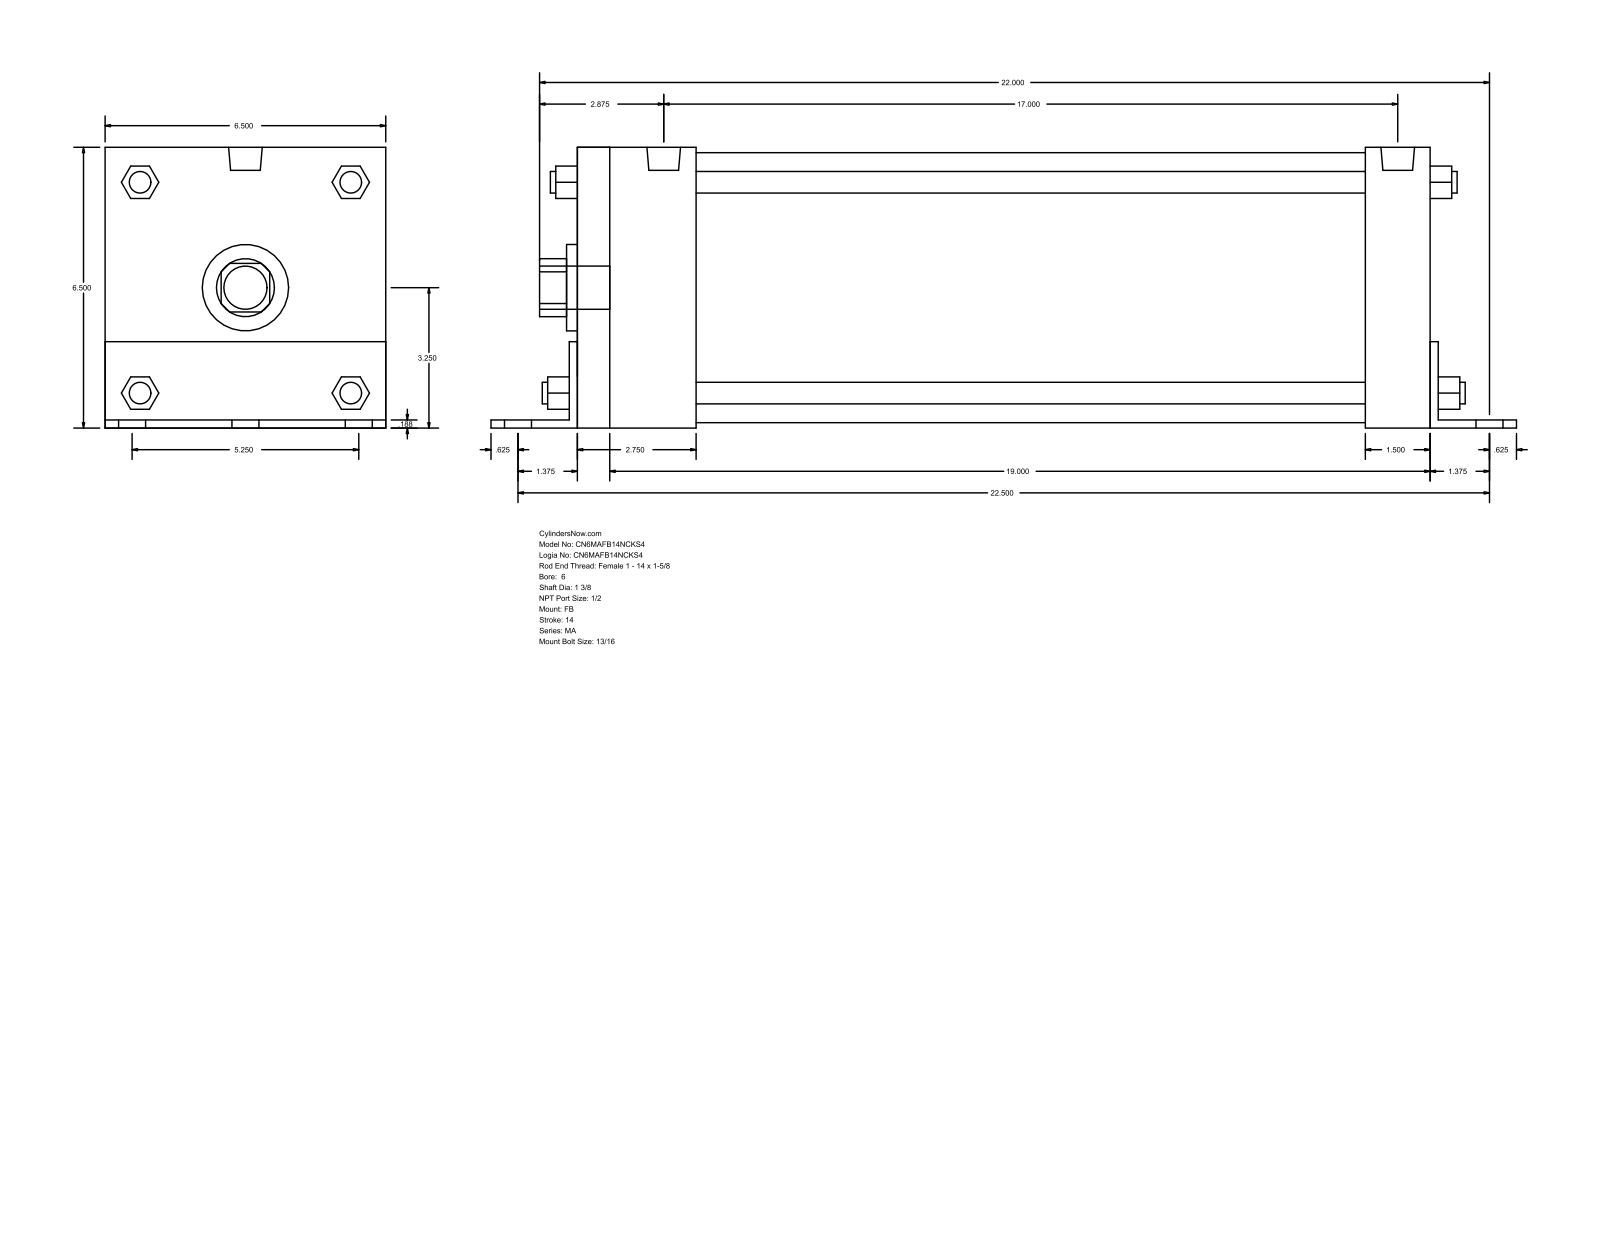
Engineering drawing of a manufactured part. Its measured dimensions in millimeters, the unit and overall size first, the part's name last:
Units: millimetres
Overall size (bounding box): 600.08 × 165.15 × 165.1
Round holes (diameter × count): ⌀34.92 ×1, ⌀50.8 ×1, ⌀158.75 ×1
Round bosses / shafts (diameter × count): ⌀20.64 ×6, ⌀17.46 ×4, ⌀12.7 ×4, ⌀19.77 ×2, ⌀25.4 ×1
Partial cylindrical surfaces — rounded edges, fillets, slot ends (radius × count): R17.06 ×1, R32.05 ×1
Main face-to-face distances: 165.1, 4.76, 498.47, 165.15, 4.71, 160.39, 4.77, 38.1, 503.24, 508
Bodies: 0 solids, 140 faces (105 planar, 35 cylindrical, 0 other)
Part name (STEP PRODUCT): MA_FB__0600_1.375
STEP written by: GSSL Pune (CONFIG_CONTROL_DESIGN)
